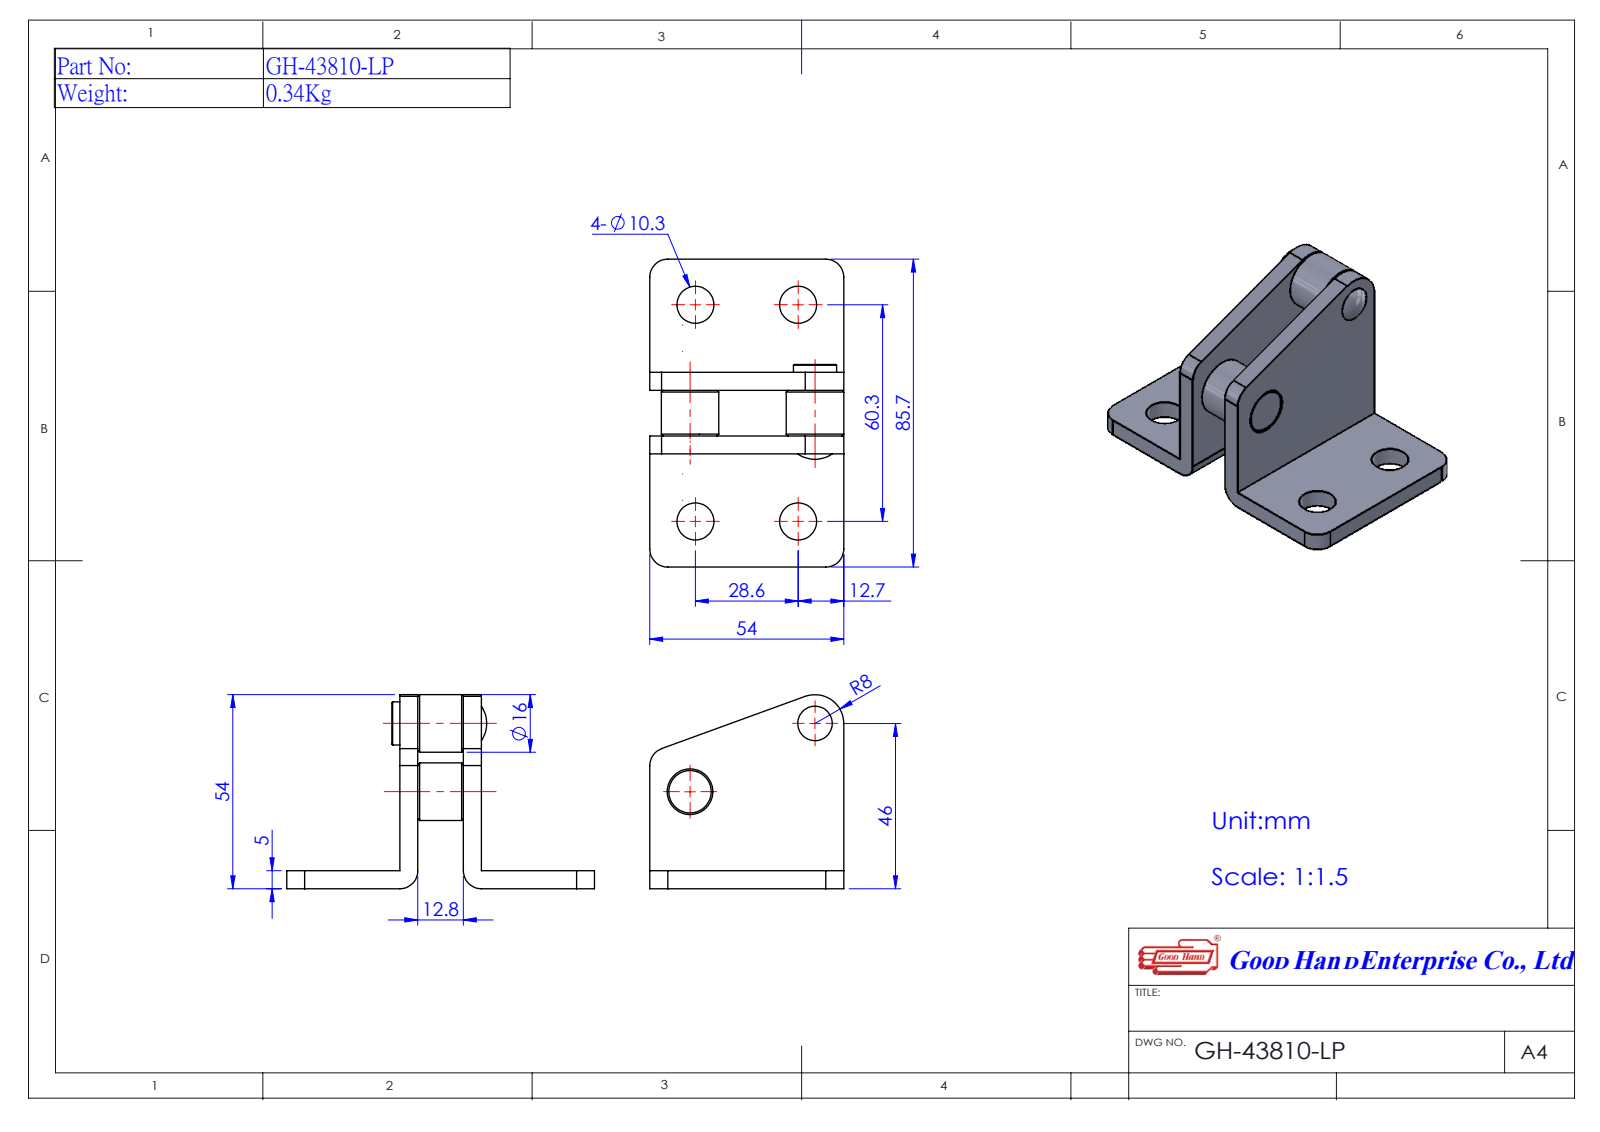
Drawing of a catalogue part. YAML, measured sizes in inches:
part_name: "Group1^GH-43810-LP(簡化); GH-43810-LP(簡化)"
step_written_by: "SolidWorks 2016 (AUTOMOTIVE_DESIGN)"
units: inches
bodies: {solids: 1, faces: 55, planar: 19, cylindrical: 30, other: 6}
overall_size: [3.378, 2.126, 2.126]
volume: 2.724
surface_area: 31.29
round_holes:
  - {diameter: 0.406, count: 4}
  - {diameter: 0.236, count: 1}
round_bosses_or_shafts:
  - {diameter: 0.63, count: 2}
  - {diameter: 0.354, count: 1}
partial_cylinders:
  - {radius: 0.197, count: 7}
face_to_face_distances: [0.197, 0.701, 0.898, 0.504, 2.126, 1.24, 1.437, 1.941, 2.138, 3.378]
hole_center_spacings: [1.126, 2.378, 2.631]
